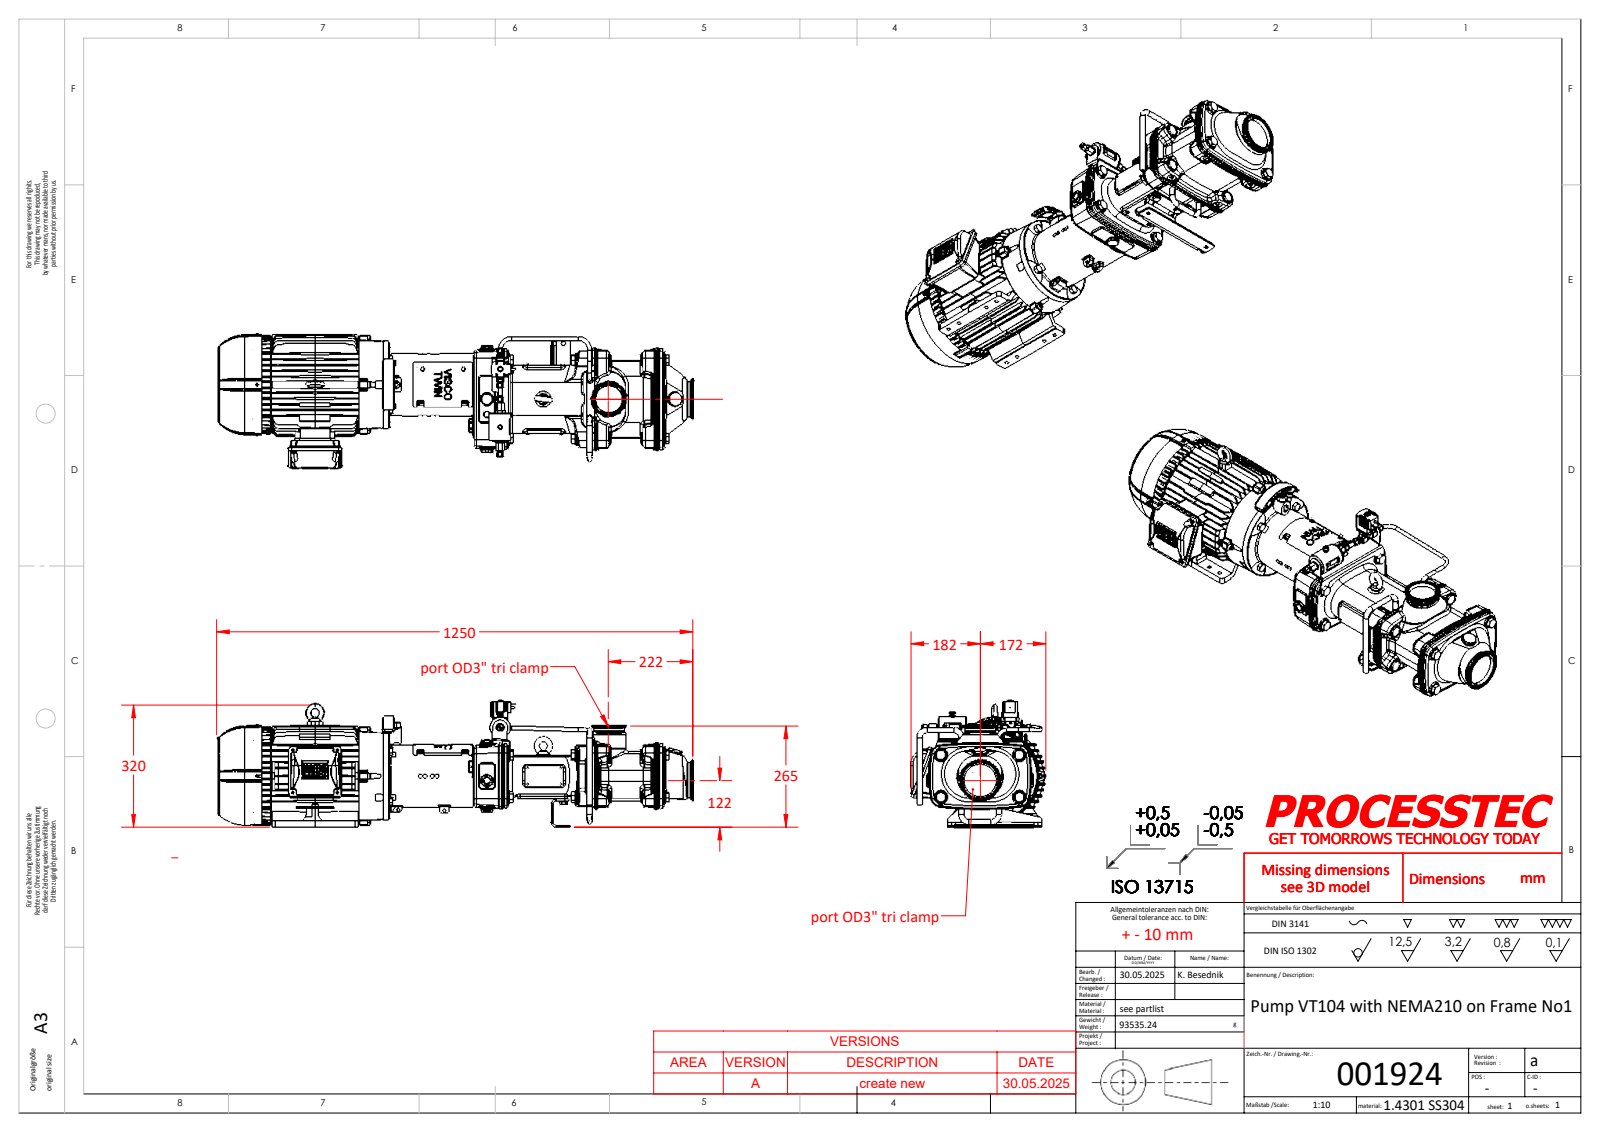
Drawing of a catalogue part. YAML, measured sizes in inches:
part_name: "001104_ISO 10642 - M6 x 16 - 16N; 001406; 001073; Rohr^001383 (+8 more)"
step_written_by: "SolidWorks 2023 (AUTOMOTIVE_DESIGN)"
units: inches
bodies: {solids: 74, faces: 9752, planar: 4223, cylindrical: 2637, other: 2892}
overall_size: [49.202, 13.931, 13.03]
volume: 2424
surface_area: 4492
round_holes:
  - {diameter: 0.315, count: 13}
  - {diameter: 0.335, count: 8}
  - {diameter: 0.41, count: 8}
  - {diameter: 0.433, count: 6}
  - {diameter: 0.157, count: 5}
  - {diameter: 0.171, count: 5}
  - {diameter: 0.197, count: 5}
  - {diameter: 0.551, count: 5}
  - {diameter: 0.689, count: 5}
  - {diameter: 0.098, count: 4}
  - {diameter: 0.422, count: 4}
  - {diameter: 0.571, count: 4}
round_bosses_or_shafts:
  - {diameter: 0.394, count: 9}
  - {diameter: 0.945, count: 8}
  - {diameter: 0.236, count: 6}
  - {diameter: 0.197, count: 6}
  - {diameter: 0.63, count: 5}
  - {diameter: 1.181, count: 4}
  - {diameter: 0.512, count: 4}
  - {diameter: 0.5, count: 4}
partial_cylinders:
  - {radius: 0.039, count: 1156}
  - {radius: 0.197, count: 82}
  - {radius: 0.059, count: 73}
  - {radius: 0.079, count: 60}
  - {radius: 0.118, count: 56}
  - {radius: 0.315, count: 36}
  - {radius: 0.236, count: 26}
  - {radius: 0.394, count: 25}
face_to_face_distances: [0.591, 1.181, 0.217, 9.106, 23.823, 14.717, 4.031, 0.807, 0.374, 39.95]
hole_center_spacings: [5.127, 2.165, 1.132, 1.5, 2.091, 2.623, 2.982, 3.615]
